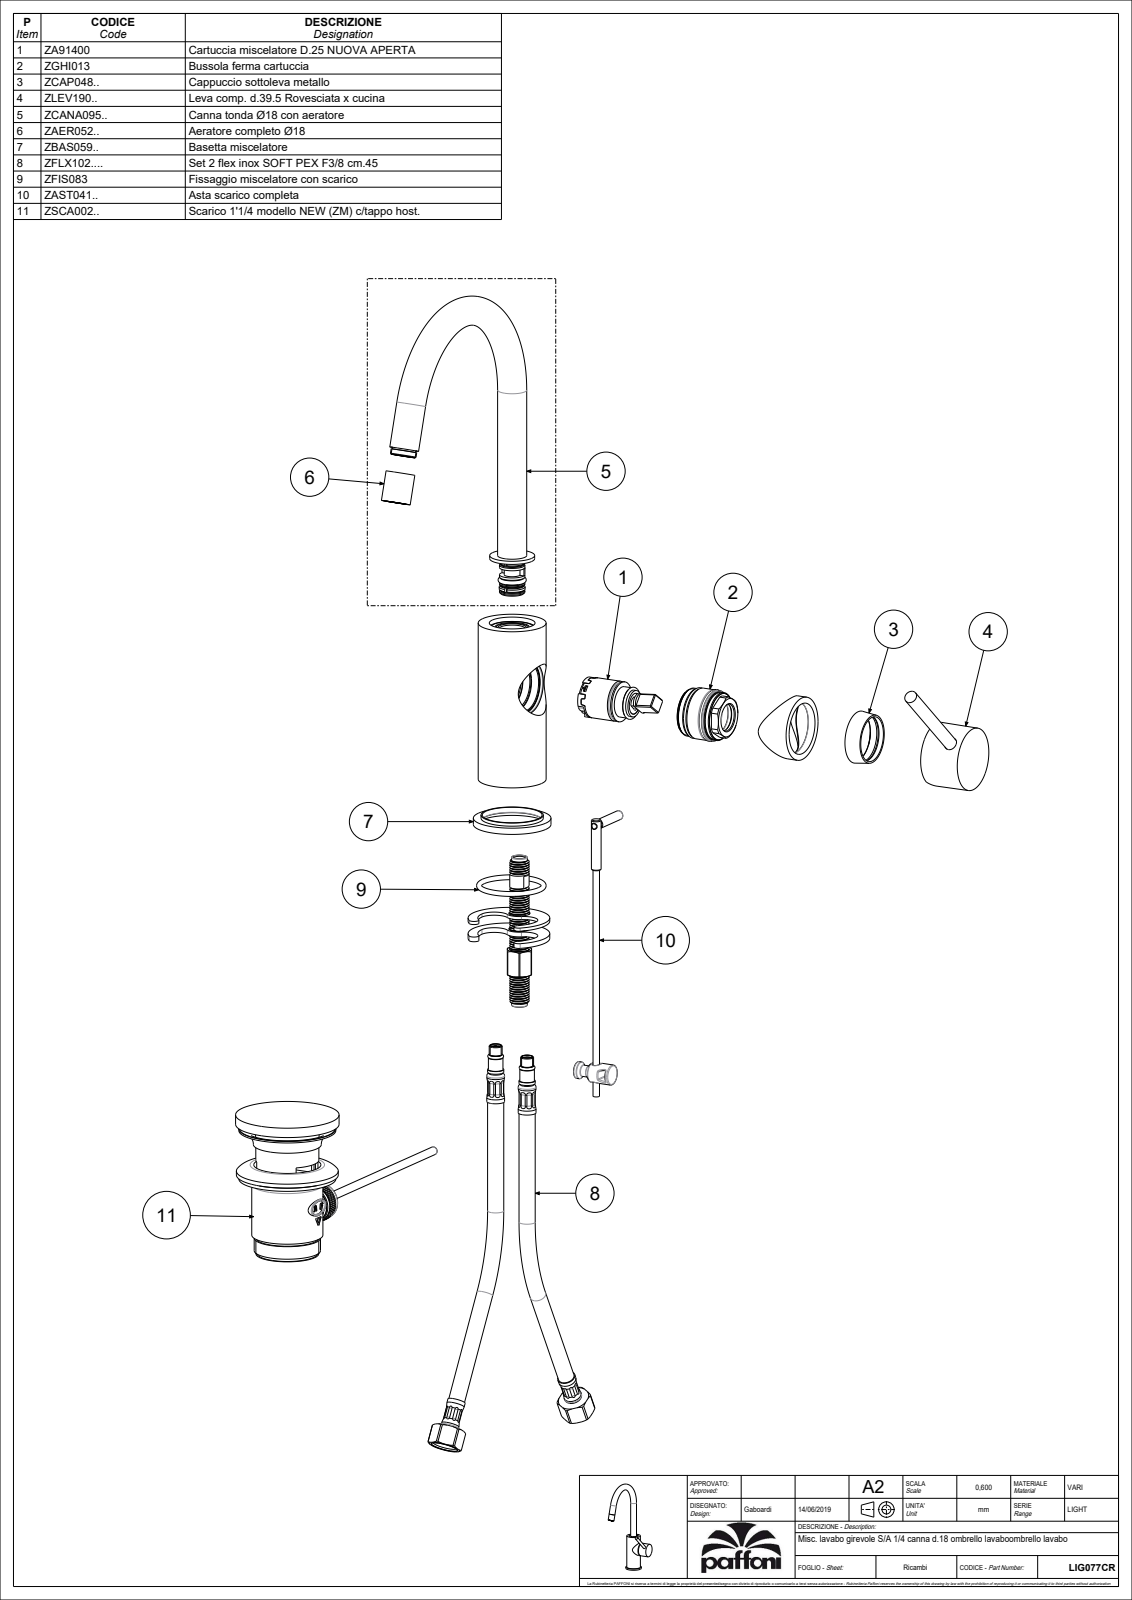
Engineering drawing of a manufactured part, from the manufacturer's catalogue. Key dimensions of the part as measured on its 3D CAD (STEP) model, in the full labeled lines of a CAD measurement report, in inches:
Part name (STEP PRODUCT): LIG077CR
STEP written by: CREO PARAMETRIC BY PTC INC, 2020044 (CONFIG_CONTROL_DESIGN)
Units: inches
Bodies: 0 solids, 116 faces (45 planar, 46 cylindrical, 25 other)
Overall size (bounding box): 11.146 × 7.604 × 3.116
Round holes (diameter × count): ⌀0.118 ×1
Round bosses / shafts (diameter × count): ⌀0.709 ×3, ⌀1.89 ×1, ⌀1.654 ×1, ⌀1.555 ×1, ⌀0.311 ×1, ⌀0.299 ×1, ⌀0.224 ×1, ⌀0.197 ×1
Partial cylindrical surfaces — rounded edges, fillets, slot ends (radius × count): R0.039 ×8, R0.031 ×2, R0.108 ×1, R0.138 ×1, R0.197 ×1, R0.252 ×1
Main face-to-face distances: 0.157, 4.094, 3.937, 0.394, 4.098, 3.941, 0.99, 0.596, 0.951, 0.557
